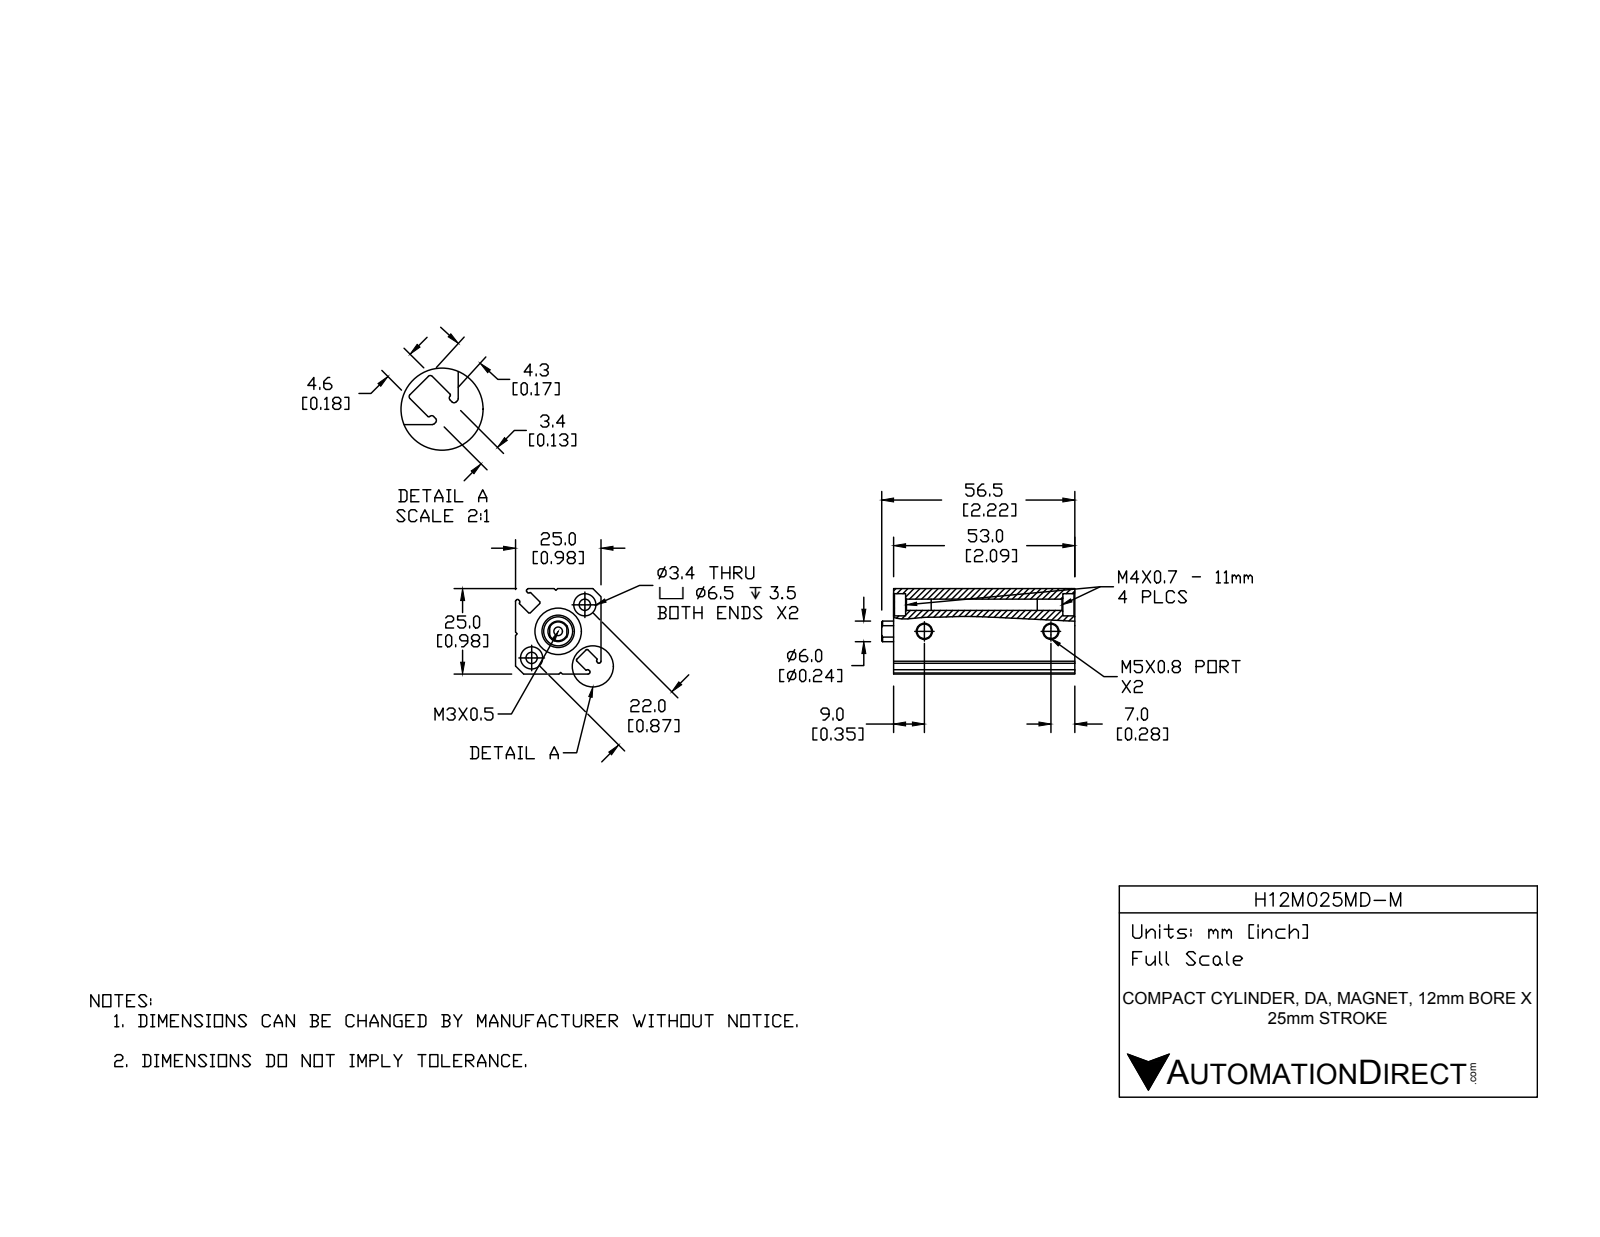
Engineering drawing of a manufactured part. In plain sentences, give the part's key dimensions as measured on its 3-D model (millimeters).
The part is named "H12M025MD-M; H12M025MD-M-PISTON; H12M025MD-M-BODY". Its 3-D file was written by "SolidWorks 2015 (CONFIG_CONTROL_DESIGN)". It is 2 solids with 128 faces: 49 planar, 54 cylindrical and 25 other. Overall it measures 56.5 by 25 by 25 millimeters. Its volume is 25 837 cubic millimeters and its surface area 12 122 square millimeters. Round holes: 2 of diameter 3.3, 2 of diameter 4.2, 2 of diameter 6.5, 1 of diameter 2.5, 1 of diameter 6, 1 of diameter 12, 1 of diameter 13.6. Round bosses or shafts: 1 of diameter 9.5. Partial cylindrical surfaces (rounded edges, fillets, slot ends): 16 of radius 0.4, 4 of radius 0.2. The main face-to-face distances are 25, 4.6, 53, 13.7, 18.3, 5.5, 47.5, 19.2, 32, 44. The hole center spacings are 11, 22.01, 37.
